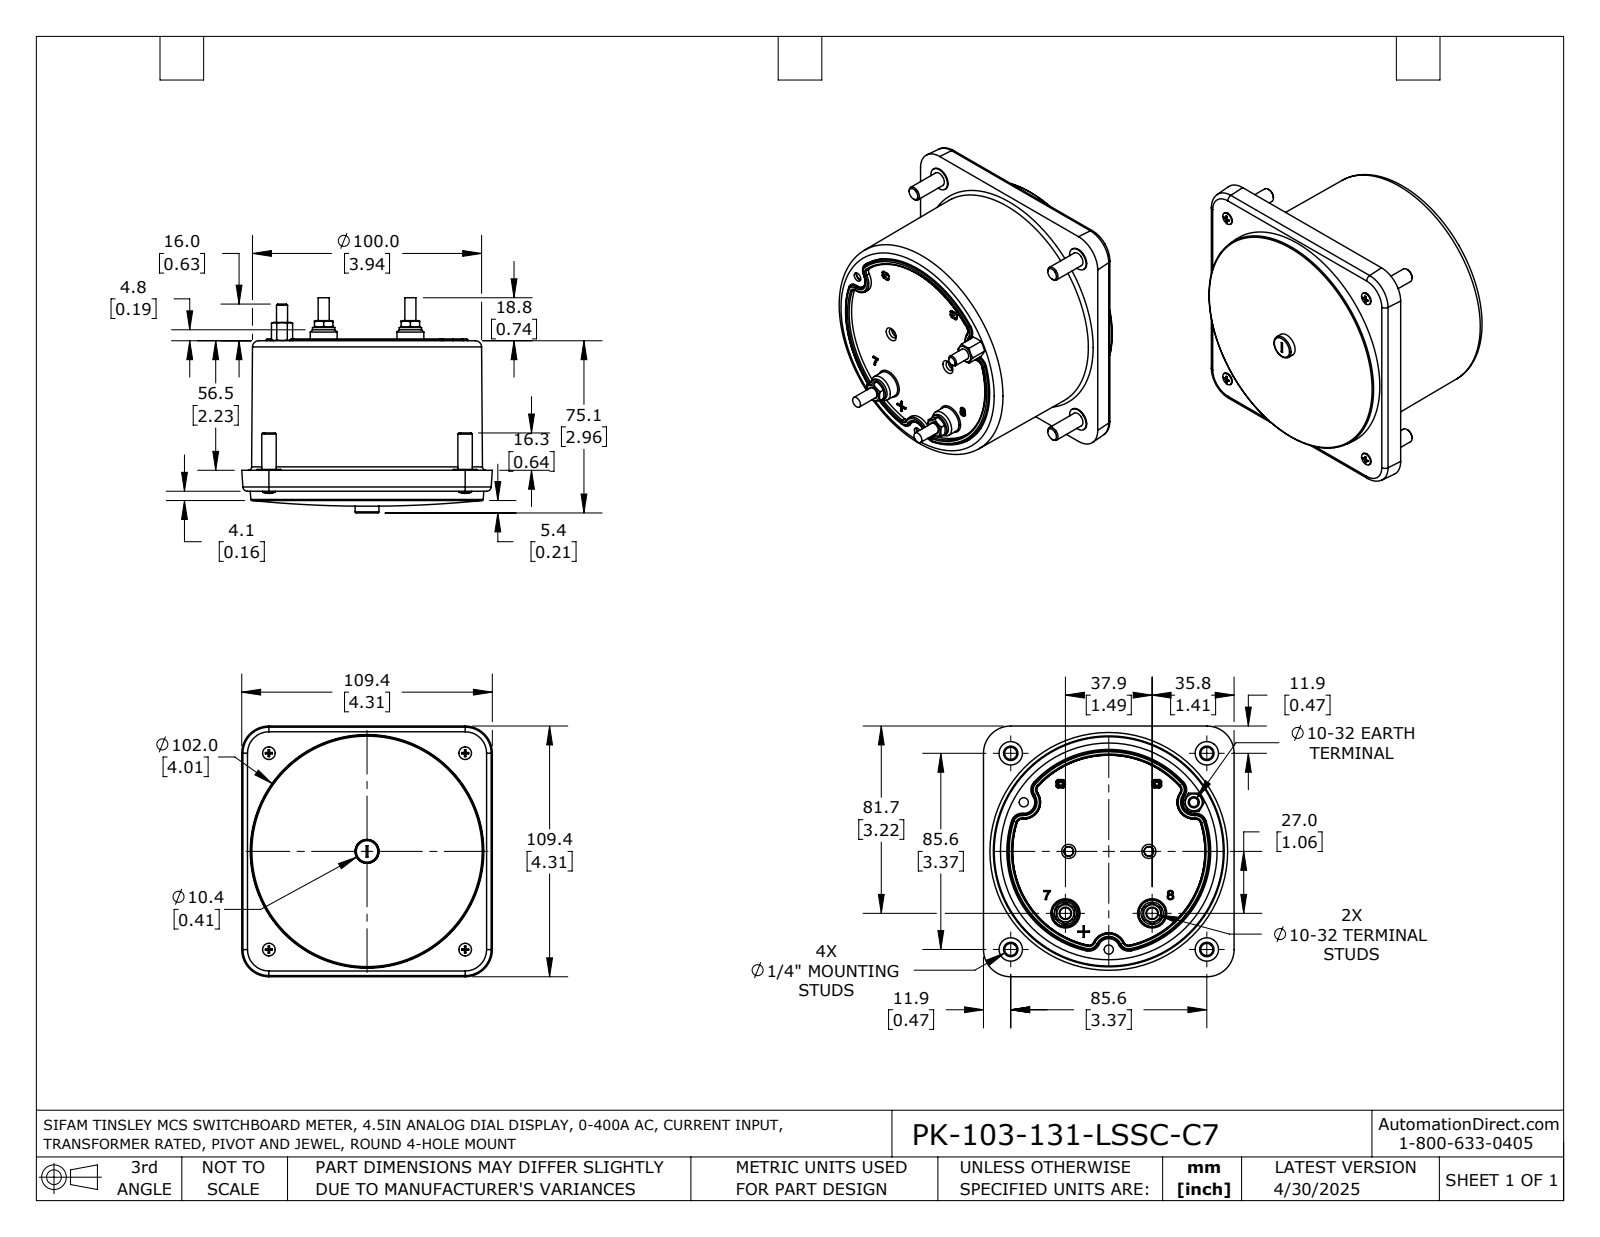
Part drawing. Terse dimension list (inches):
name: PK-103-131-LSSC-C7
written by: SolidWorks 2021 (AUTOMOTIVE_DESIGN)
unit: in
bodies: 1 solid, 609 faces (167 planar, 141 cylindrical, 301 other)
size: 4.307 × 4.307 × 3.697
volume: 36.28 in³; area: 82.21 in²
holes: 4× ⌀0.094, 4× ⌀0.138, 4× ⌀0.315, 3× ⌀0.157, 2× ⌀0.209
bosses: 4× ⌀0.402, 4× ⌀0.248, 4× ⌀0.217, 4× ⌀0.114, 3× ⌀0.19, 2× ⌀0.384, 1× ⌀0.146
rounds: 24× R0.02, 9× R0.189, 4× R0.079, 1× R1.752
face distances: 2.177, 2.537, 0.36, 0.048, 2.225, 2.585, 0.489, 2.715, 2.667, 0.129
hole spacings: 3.372, 3.37, 3.374, 3.378, 3.38, 4.769, 0.971, 1.126
